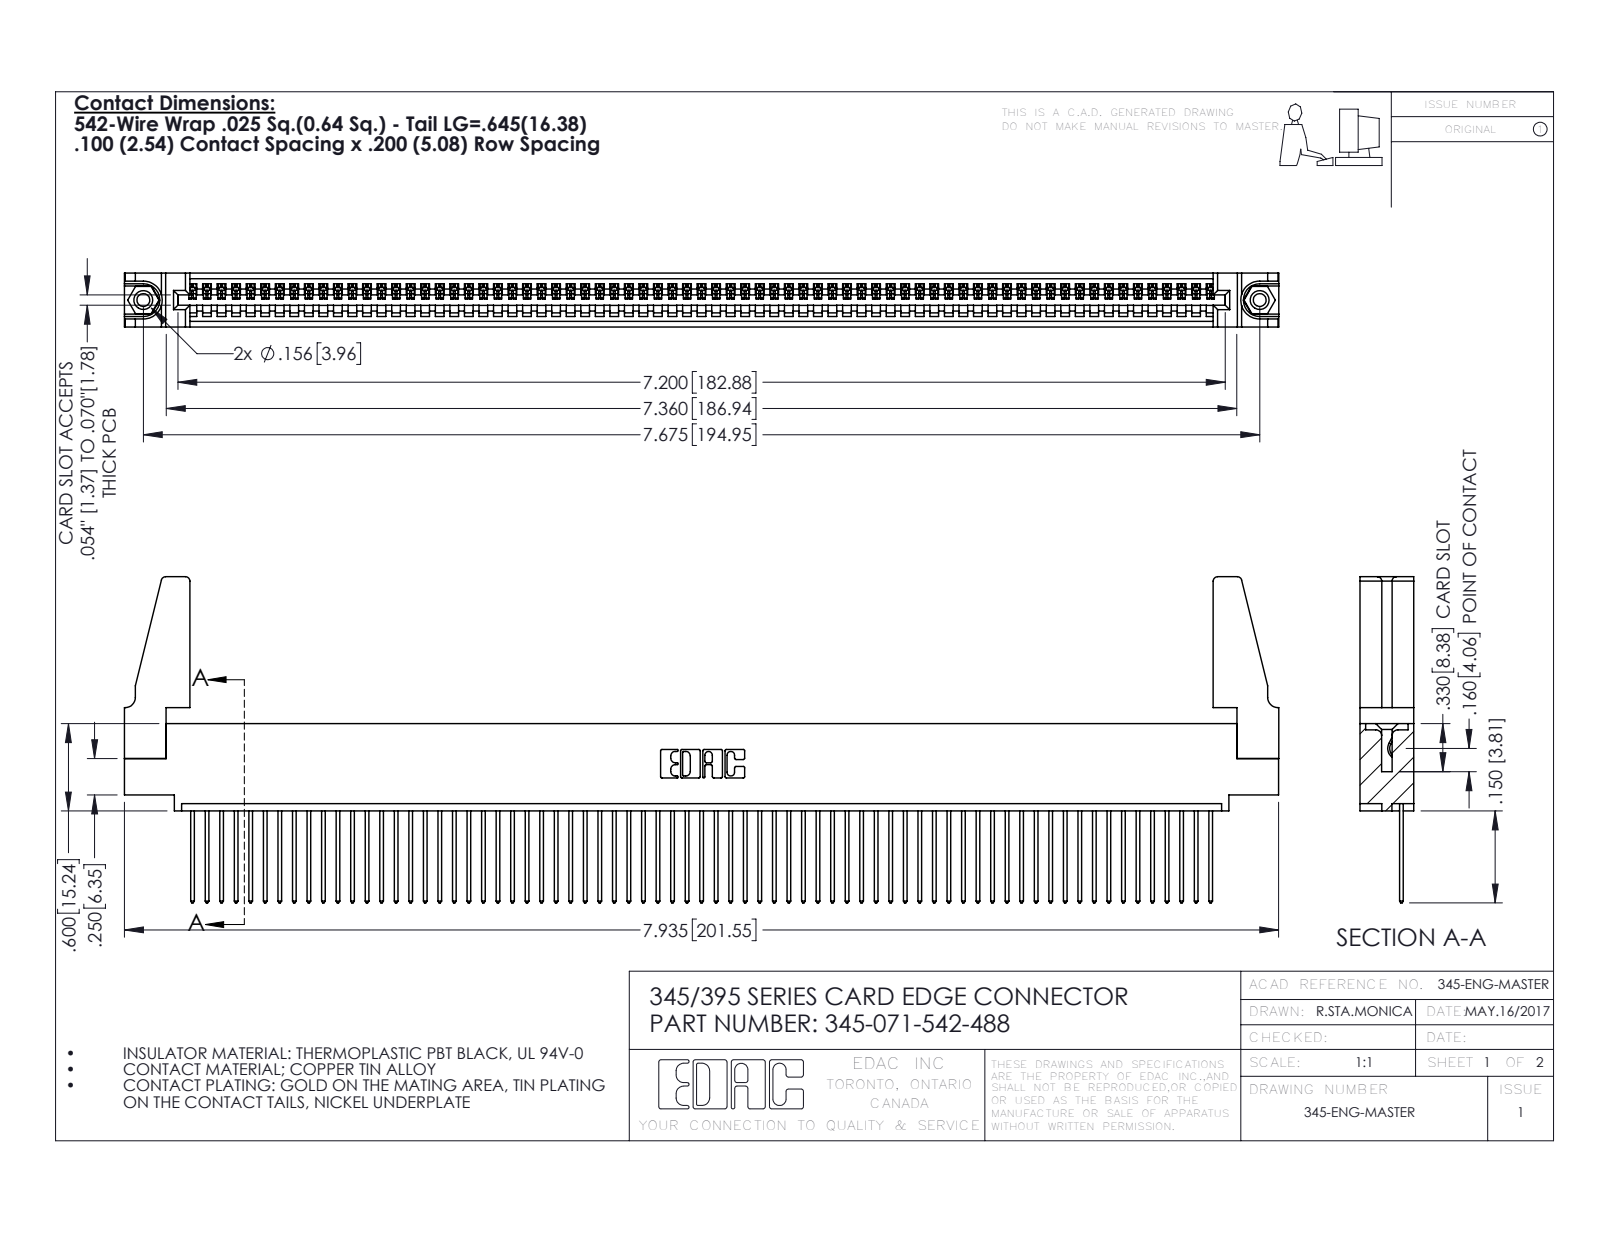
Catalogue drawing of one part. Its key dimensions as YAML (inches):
part_name: "345-220-078_345-220-088; 345-292-001_345-293-142; 345-250-001_345-250-001-102; 345-071-542-488 (+1 more)"
step_written_by: "SolidWorks 2016 (CONFIG_CONTROL_DESIGN)"
units: inches
bodies: {solids: 76, faces: 4372, planar: 2996, cylindrical: 1360, other: 16}
overall_size: [7.936, 2.242, 0.37]
volume: 1.386
surface_area: 47.24
round_holes:
  - {diameter: 0.089, count: 2}
  - {diameter: 0.125, count: 2}
  - {diameter: 0.156, count: 2}
  - {diameter: 0.064, count: 1}
round_bosses_or_shafts:
  - {diameter: 0.155, count: 2}
partial_cylinders:
  - {radius: 0.006, count: 142}
  - {radius: 0.01, count: 142}
  - {radius: 0.01, count: 22}
  - {radius: 0.03, count: 8}
  - {radius: 0.007, count: 6}
  - {radius: 0.031, count: 6}
  - {radius: 0.026, count: 3}
  - {radius: 0.031, count: 2}
face_to_face_distances: [0.072, 0.298, 0.37, 0.098, 0.272, 0.025, 0.2, 0.225, 0.149, 0.072]
hole_center_spacings: [0.27, 7.439, 7.675]
